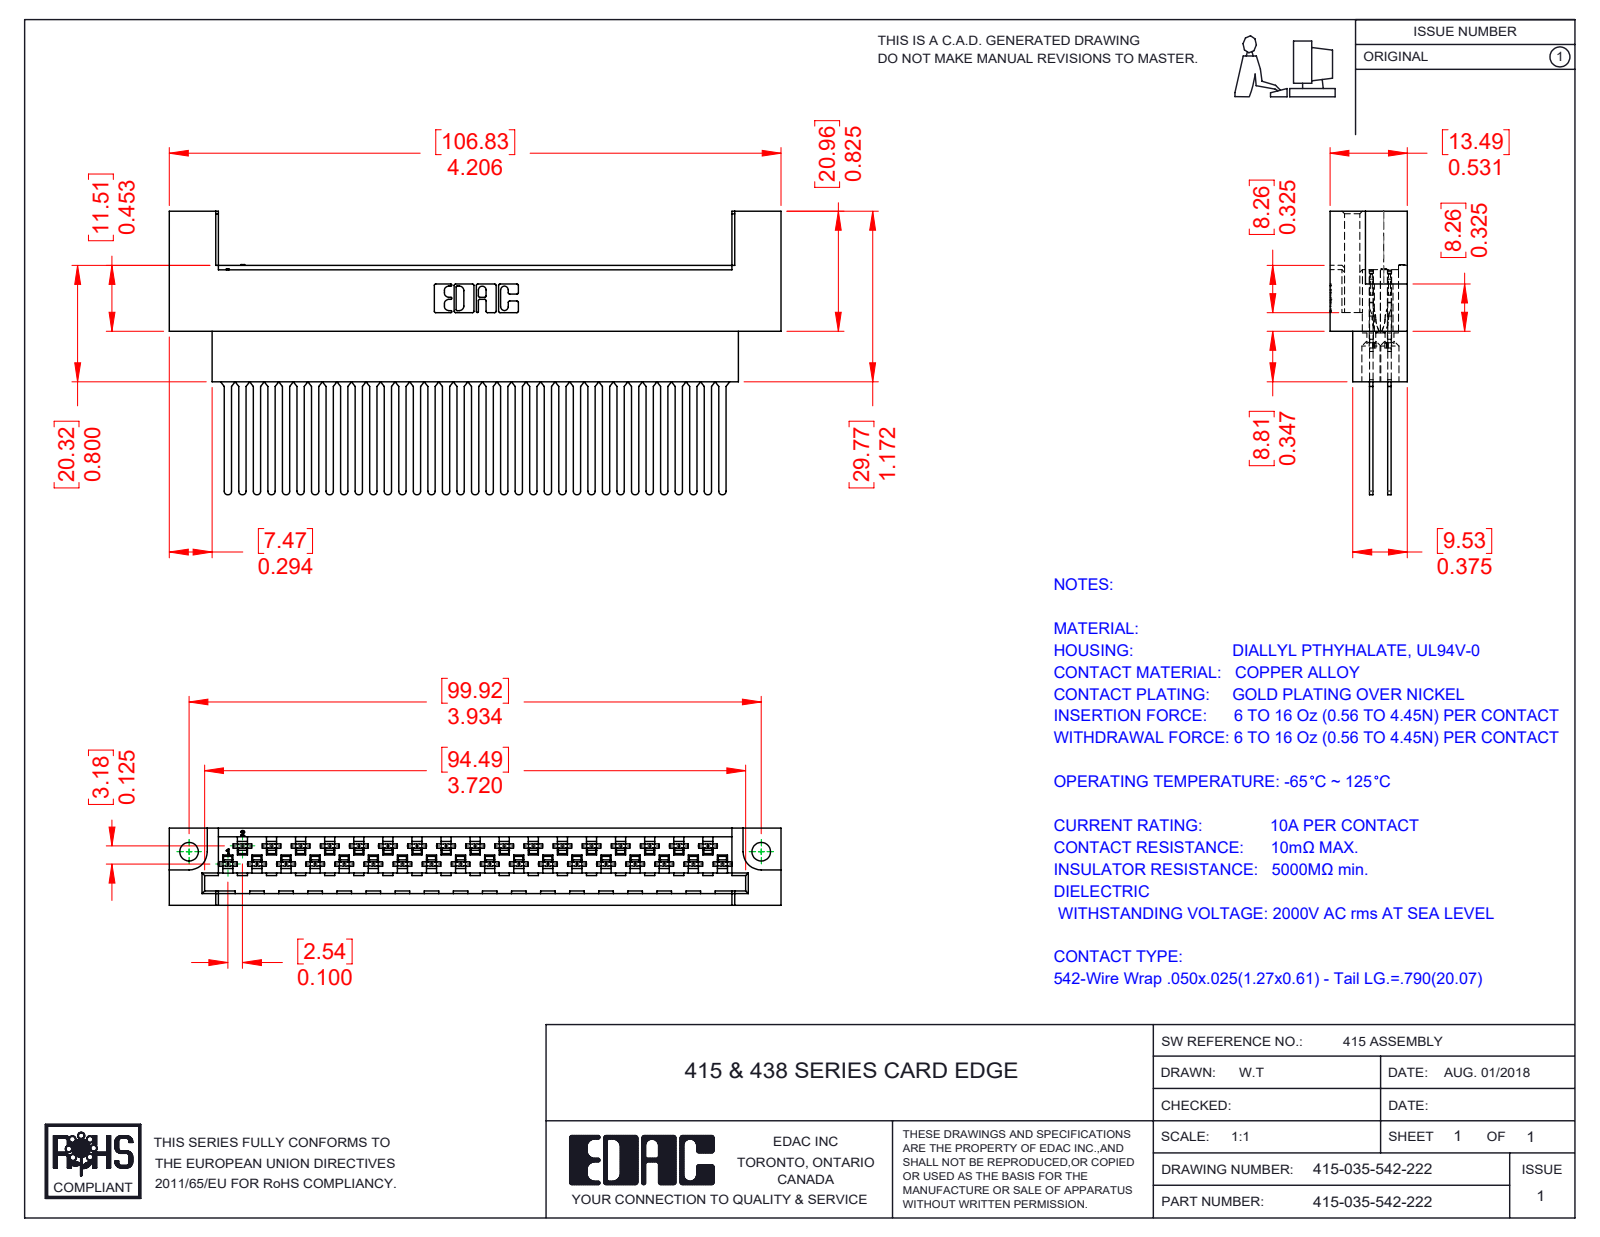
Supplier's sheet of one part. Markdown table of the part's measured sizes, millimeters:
| quantity | value |
| --- | --- |
| part name | 415-210-001_415-210-035-222; 516-290-001_542; 415-035-542-222 |
| STEP written by | SolidWorks 2016 (CONFIG_CONTROL_DESIGN) |
| units | millimeters |
| bodies | 36 solids, 3590 faces (2297 planar, 956 cylindrical, 337 other) |
| overall size | 106.83 × 49.49 × 13.49 |
| volume | 18 807 mm³ |
| surface area | 25 109 mm² |
| round holes (diameter × count) | 1.27 × 35, 3.3 × 35, 3.25 × 2 |
| partial cylindrical surfaces (radius × count) | 0.3 × 140, 0.56 × 140, 0.18 × 70, 0.2 × 70, 0.41 × 70, 2.03 × 70, 0.64 × 35, 0.25 × 22 |
| main face-to-face distances | 3.18, 0.61, 7.49, 13.49, 6.61, 6.88, 6, 1.27, 1.88, 2.82 |
| hole center spacings | 5.08, 10.16, 15.24, 20.32, 25.4, 30.48, 35.56, 2.54 |
